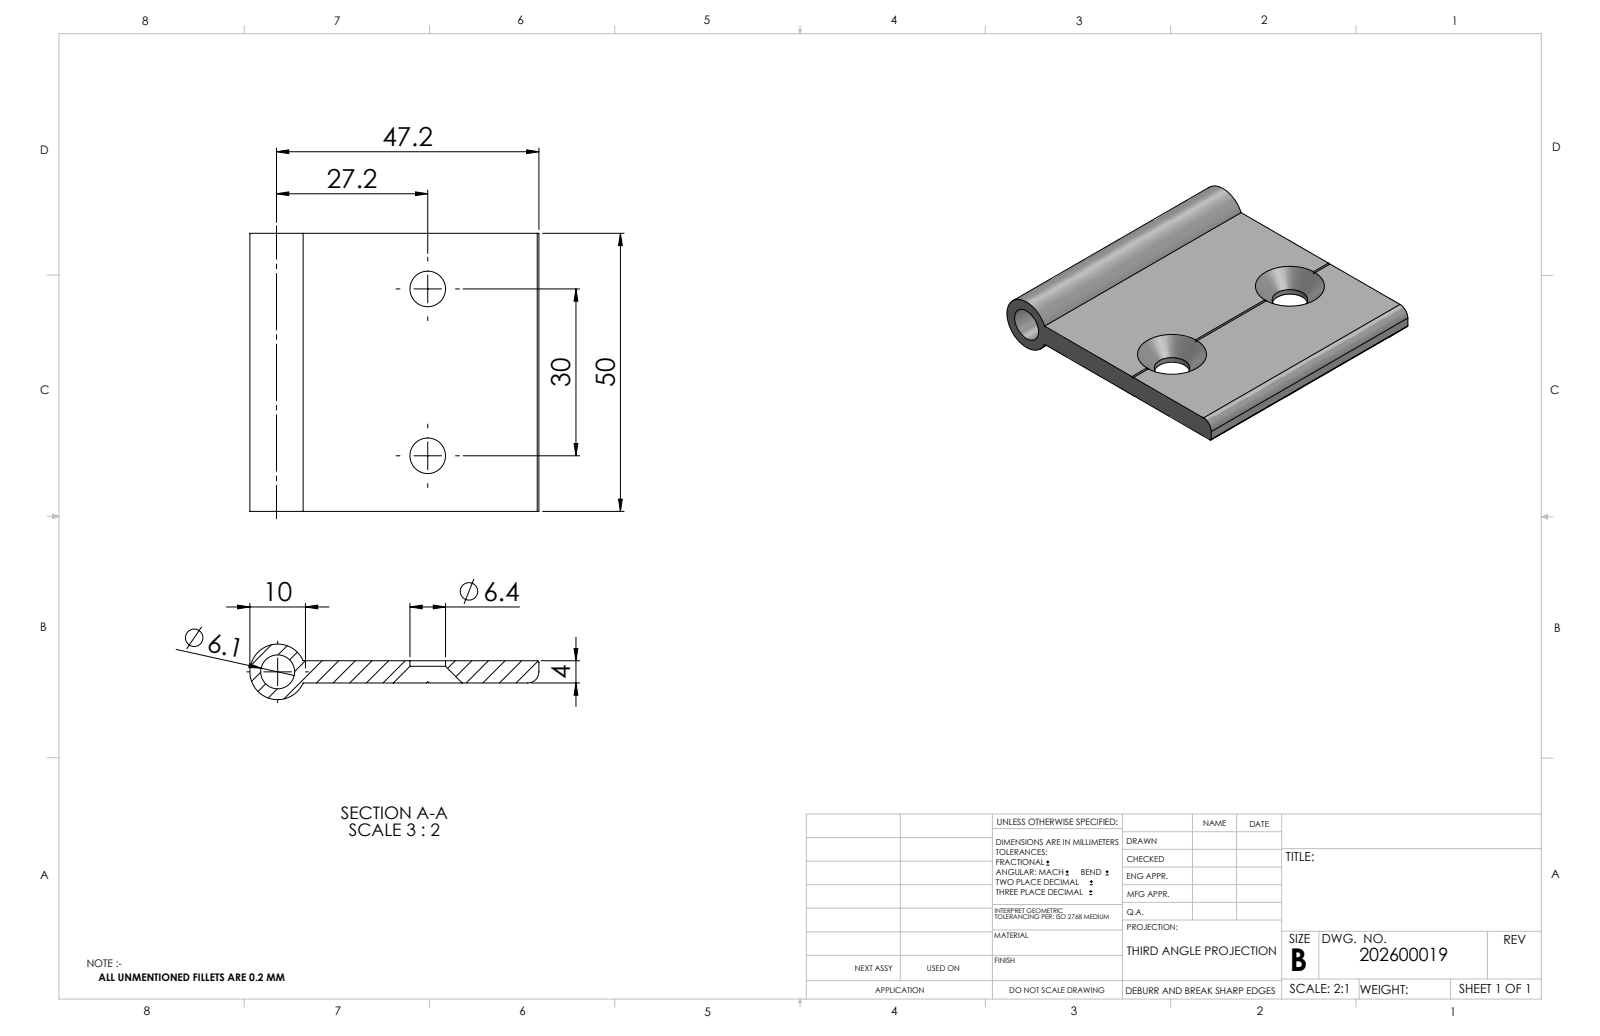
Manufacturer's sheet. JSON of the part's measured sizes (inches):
{"part_name": "202600019_c_1", "step_written_by": "SolidWorks 2014 (CONFIG_CONTROL_DESIGN)", "units": "inches", "bodies": {"solids": 1, "faces": 26, "planar": 12, "cylindrical": 10, "other": 4}, "overall_size": [2.047, 1.969, 0.394], "volume_in3": 0.632, "surface_area_in2": 11.07, "round_holes": [[0.252, 2], [0.24, 1]], "round_bosses_or_shafts": [[0.394, 1]], "partial_cylinders_radius": [[0.012, 1], [0.079, 1]], "face_to_face_distances": [0.157, 1.969], "hole_center_spacings": [1.181]}
